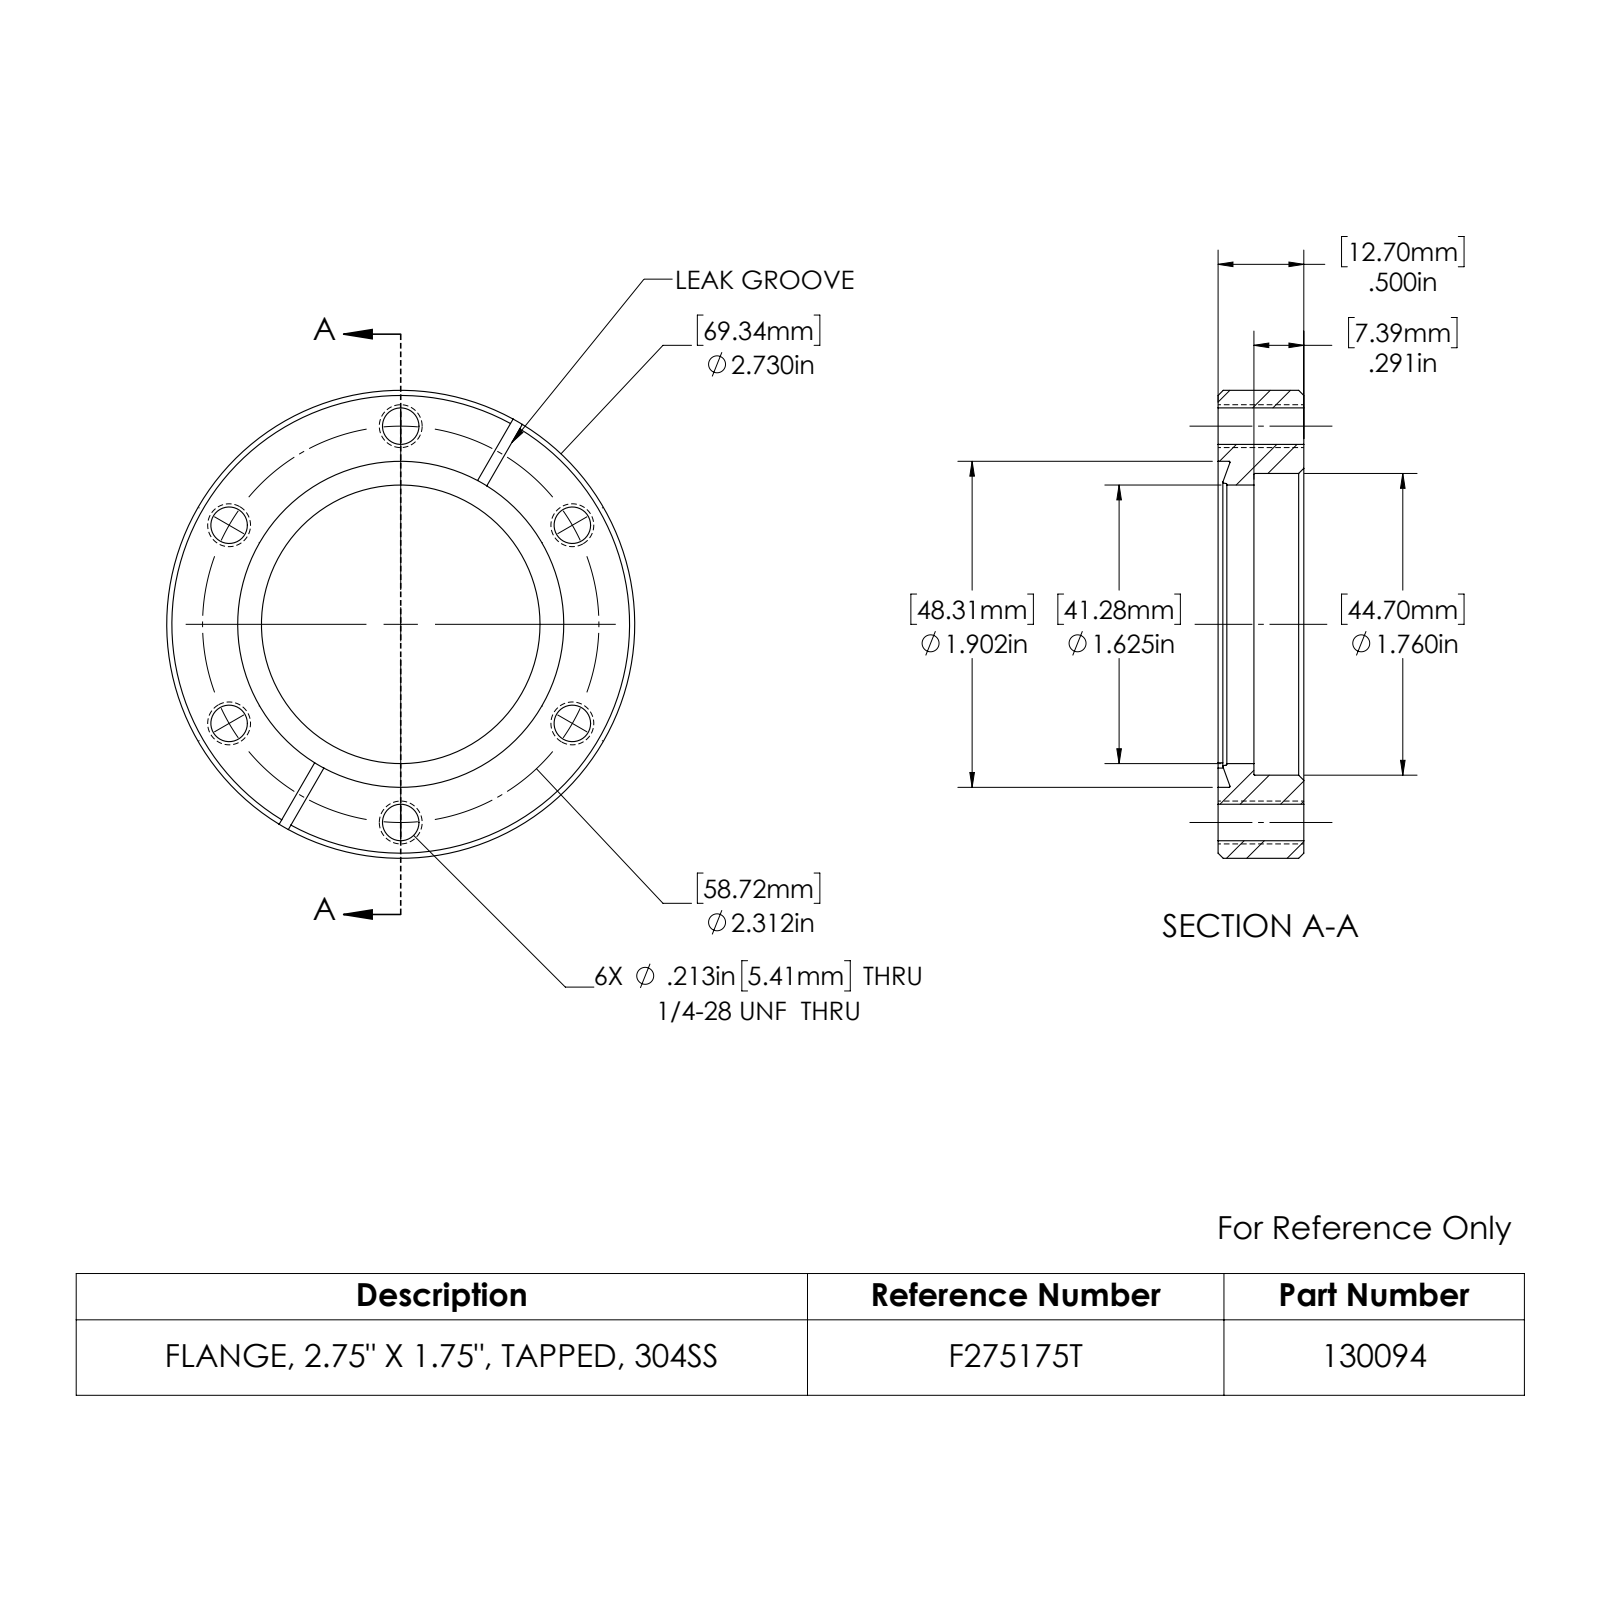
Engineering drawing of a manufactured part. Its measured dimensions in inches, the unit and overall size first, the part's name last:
Units: inches
Overall size (bounding box): 2.73 × 2.73 × 0.5
Round holes (diameter × count): ⌀0.213 ×6, ⌀1.625 ×1, ⌀1.76 ×1, ⌀1.902 ×1
Round bosses / shafts (diameter × count): ⌀2.73 ×1
Main face-to-face distances: 0.5, 0.209, 0.291, 0.052, 0.157, 0.448, 0.062, 0.051, 0.158, 0.449
Hole centre spacings: 1.156, 2.002, 2.002, 2.312, 2.312
Volume: 1.628 in³ · Surface area: 16.04 in²
Bodies: 1 solid, 50 faces (11 planar, 20 cylindrical, 19 other)
Part name (STEP PRODUCT): 130094
STEP written by: SolidWorks 2022 (AUTOMOTIVE_DESIGN)
